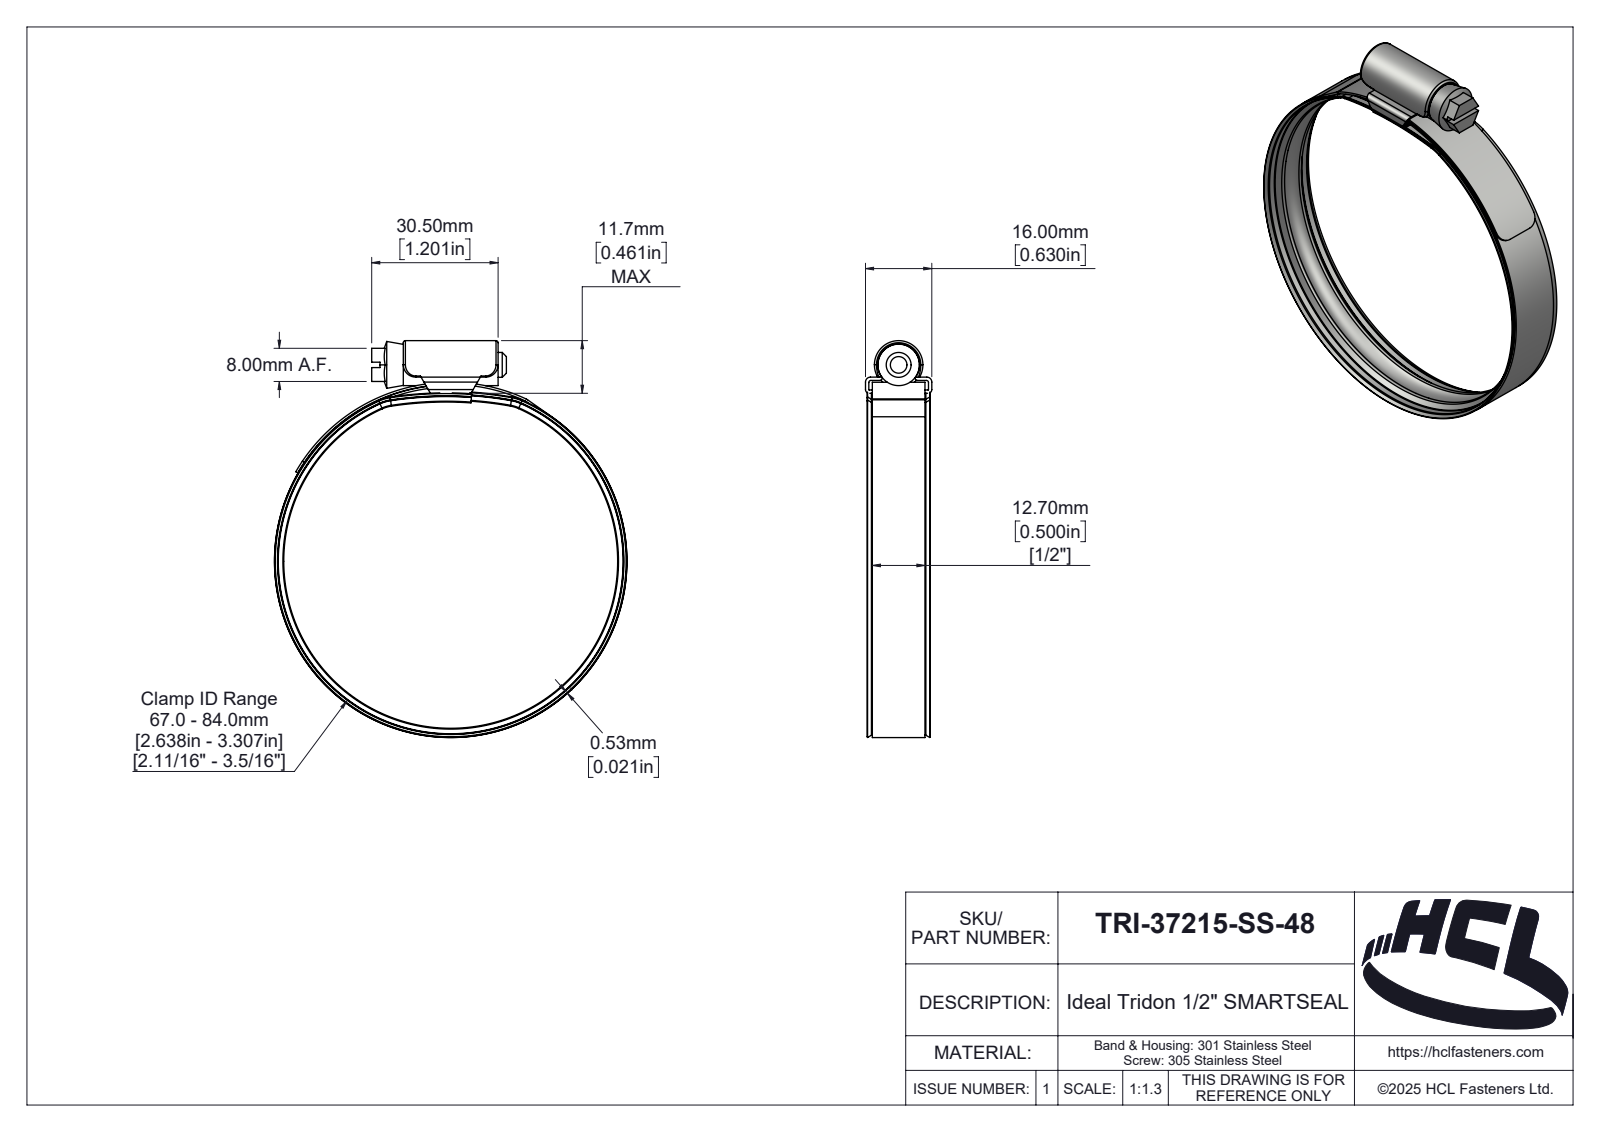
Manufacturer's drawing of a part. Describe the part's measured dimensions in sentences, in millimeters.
The part is named "TRI-37215-SS-48". Its 3-D file was written by "SolidWorks 2025 (AUTOMOTIVE_DESIGN)". It is 4 solids with 418 faces: 42 planar, 119 cylindrical and 257 other. Overall it measures 95.73 by 85.06 by 16 millimeters. Its volume is 6 059 cubic millimeters and its surface area 20 422 square millimeters. Round holes: 1 of diameter 83.4, 1 of diameter 84. Round bosses or shafts: 1 of diameter 85.06, 1 of diameter 83.8, 1 of diameter 10, 1 of diameter 6. Partial cylindrical surfaces (rounded edges, fillets, slot ends): 6 of radius 0.5, 4 of radius 3, 2 of radius 0.1, 2 of radius 0.9, 2 of radius 1.2, 2 of radius 9.9, 2 of radius 10.1, 1 of radius 0.46. The main face-to-face distances are 0.8, 12.7, 3.1, 0.54, 2.3, 30.5, 3.9, 1.65, 14.35, 15.2.
